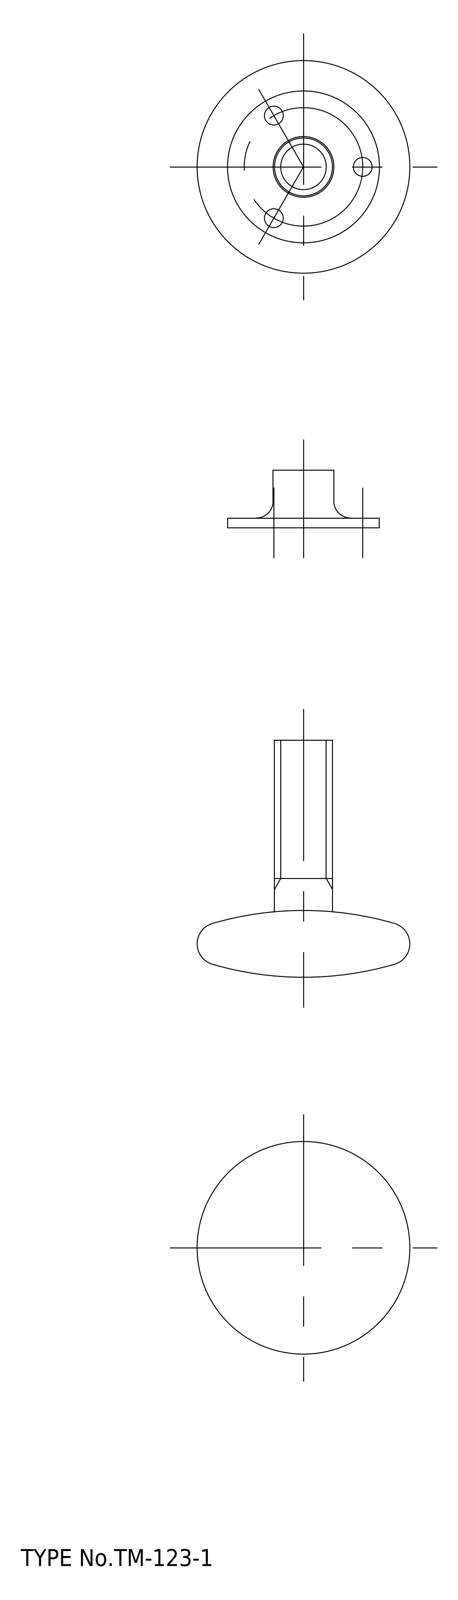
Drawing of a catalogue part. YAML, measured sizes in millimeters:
part_name: "nut; foot; bolt"
step_written_by: "spGate 17.5.1 (AUTOMOTIVE_DESIGN)"
units: millimeters
bodies: {solids: 3, faces: 28, planar: 6, cylindrical: 16, other: 6}
overall_size: [39, 35, 35]
volume: 9902
surface_area: 4913
round_holes:
  - {diameter: 3.1, count: 3}
  - {diameter: 9.53, count: 1}
round_bosses_or_shafts:
  - {diameter: 25, count: 1}
  - {diameter: 10, count: 1}
face_to_face_distances: [1.6, 14.82, 16.42, 31, 16.18, 14.58, 24.32, 9.5, 7.9, 6.68]
hole_center_spacings: [9.75, 16.89, 16.88]
